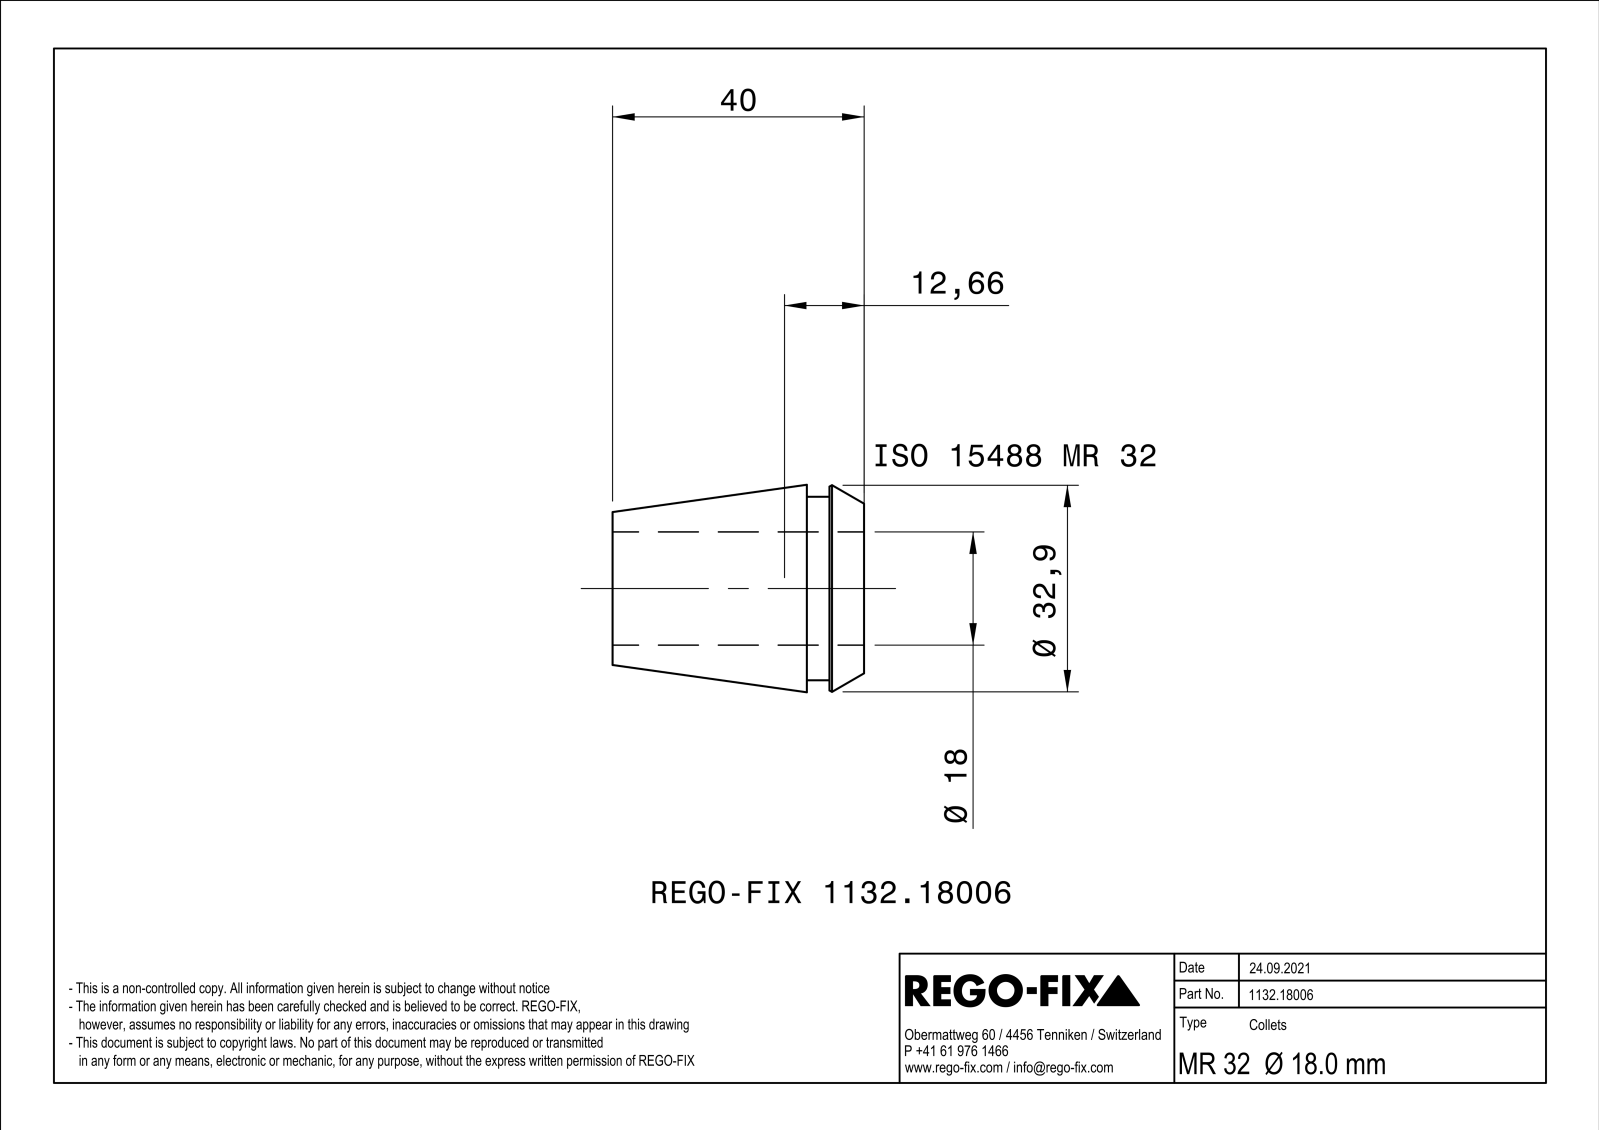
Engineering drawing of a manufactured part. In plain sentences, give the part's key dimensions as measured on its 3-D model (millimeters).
The part is named "NOCUT". Its 3-D file was written by "SIEMENS PLM Software Solid Edge ST10 (AUTOMOTIVE_DESIGN)". It is 1 solid with 209 faces: 88 planar, 41 cylindrical and 80 other. Overall it measures 40 by 32.98 by 32.98 millimeters. Its volume is 13 134 cubic millimeters and its surface area 11 888 square millimeters. Round holes: 1 of diameter 18. Round bosses or shafts: 1 of diameter 29.2. Partial cylindrical surfaces (rounded edges, fillets, slot ends): 20 of radius 0.4. The main face-to-face distances are 1, 40, 9.1, 30.9, 5.5, 3.6, 34.5, 6, 0.5, 3.1.
